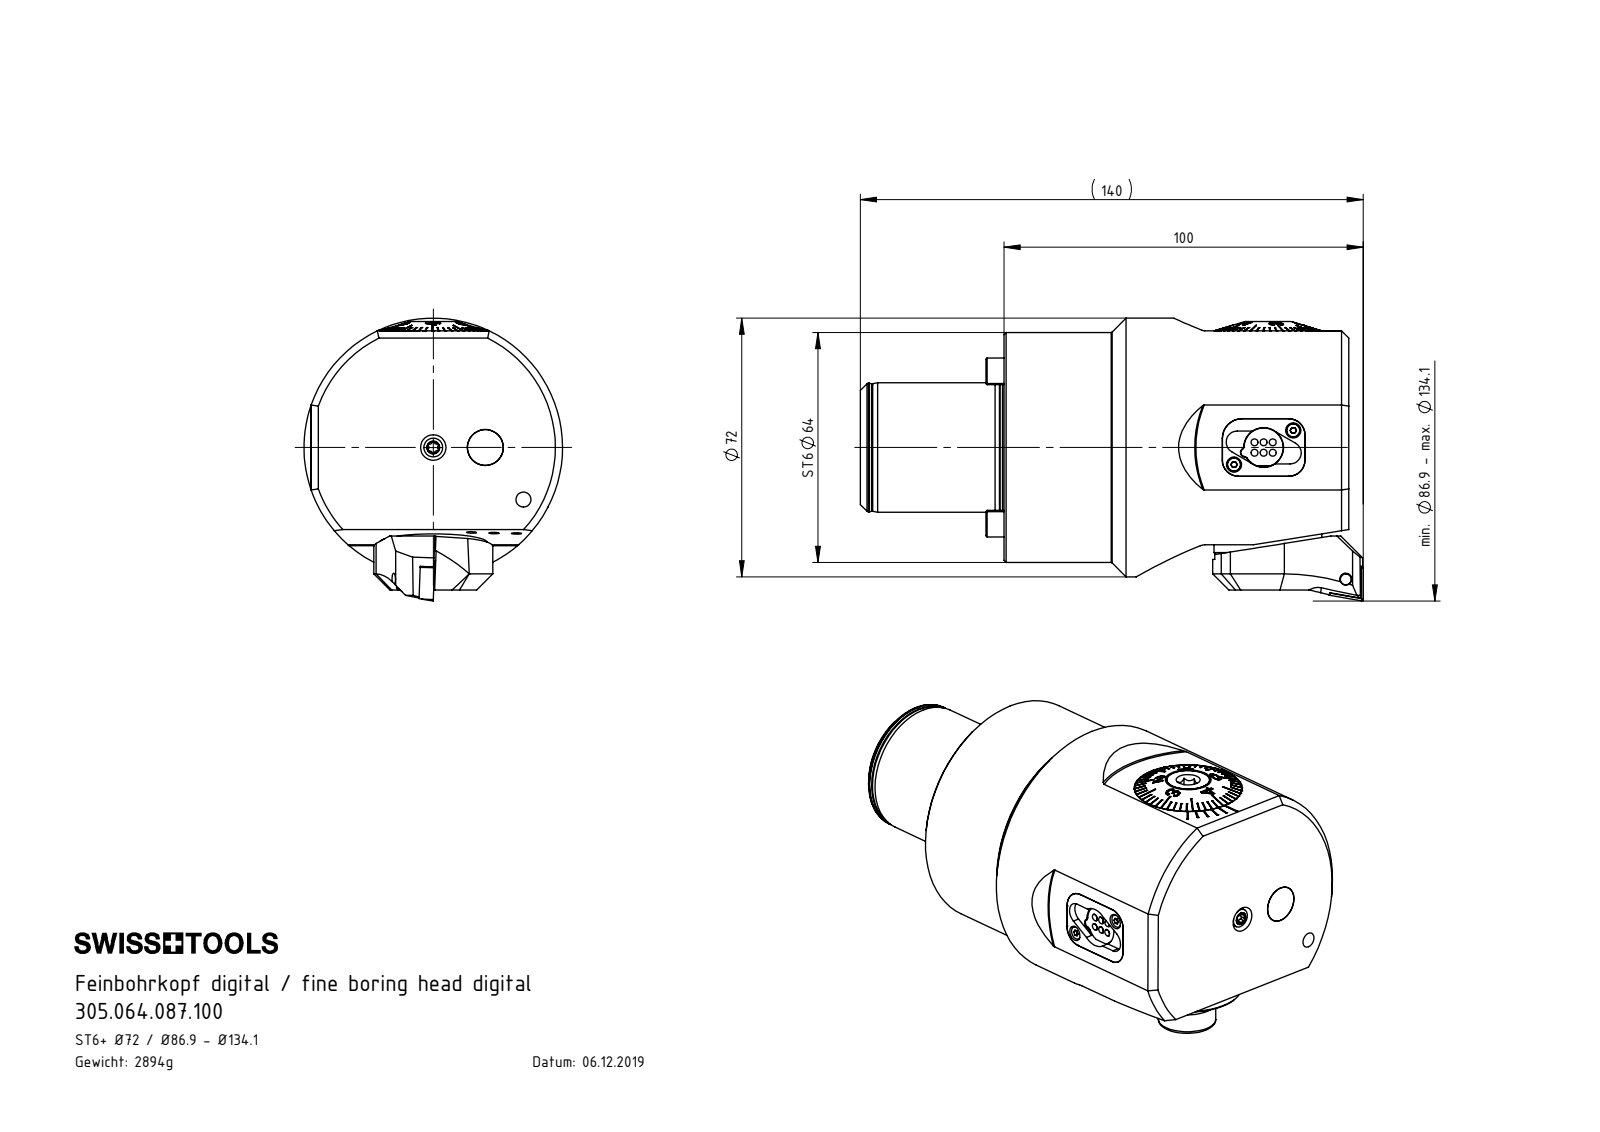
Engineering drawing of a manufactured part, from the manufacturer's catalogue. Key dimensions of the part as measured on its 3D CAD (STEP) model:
Part name (STEP PRODUCT): A55-BG2.012.006_B; ST6-ER2.001.012_A; A55-BG3.011.033_A_gekrzt; ISO 4026 - M10 x 16 (+8 more)
STEP written by: SolidWorks 2017 (CONFIG_CONTROL_DESIGN)
Units: millimetres
Bodies: 33 solids, 1063 faces (472 planar, 244 cylindrical, 347 other)
Overall size (bounding box): 136 × 75.66 × 72
Volume: 363 219 mm³ · Surface area: 66 767 mm²
Round holes (diameter × count): ⌀4.2 ×5, ⌀8.5 ×4, ⌀2.5 ×3, ⌀5 ×3, ⌀1.6 ×2, ⌀2.2 ×2, ⌀3.3 ×2, ⌀13 ×2, ⌀8 ×1, ⌀9.5 ×1, ⌀10 ×1, ⌀11.1 ×1
Round bosses / shafts (diameter × count): ⌀1.9 ×6, ⌀10 ×2, ⌀3.8 ×2, ⌀2 ×2, ⌀72 ×1, ⌀64 ×1, ⌀36 ×1, ⌀35.8 ×1
Partial cylindrical surfaces — rounded edges, fillets, slot ends (radius × count): R0.34 ×6, R0.5 ×6, R0.59 ×6, R1.1 ×6, R1.2 ×6, R2 ×6, R2.5 ×6, R3.2 ×3
Main face-to-face distances: 96, 53.01, 2.6, 62.11, 59.51, 6.5, 1.2, 2.8, 58.31, 5.3
Hole centre spacings: 9.52, 21.5, 25.93, 1.21, 8.49, 10.59, 14.5, 17.97
